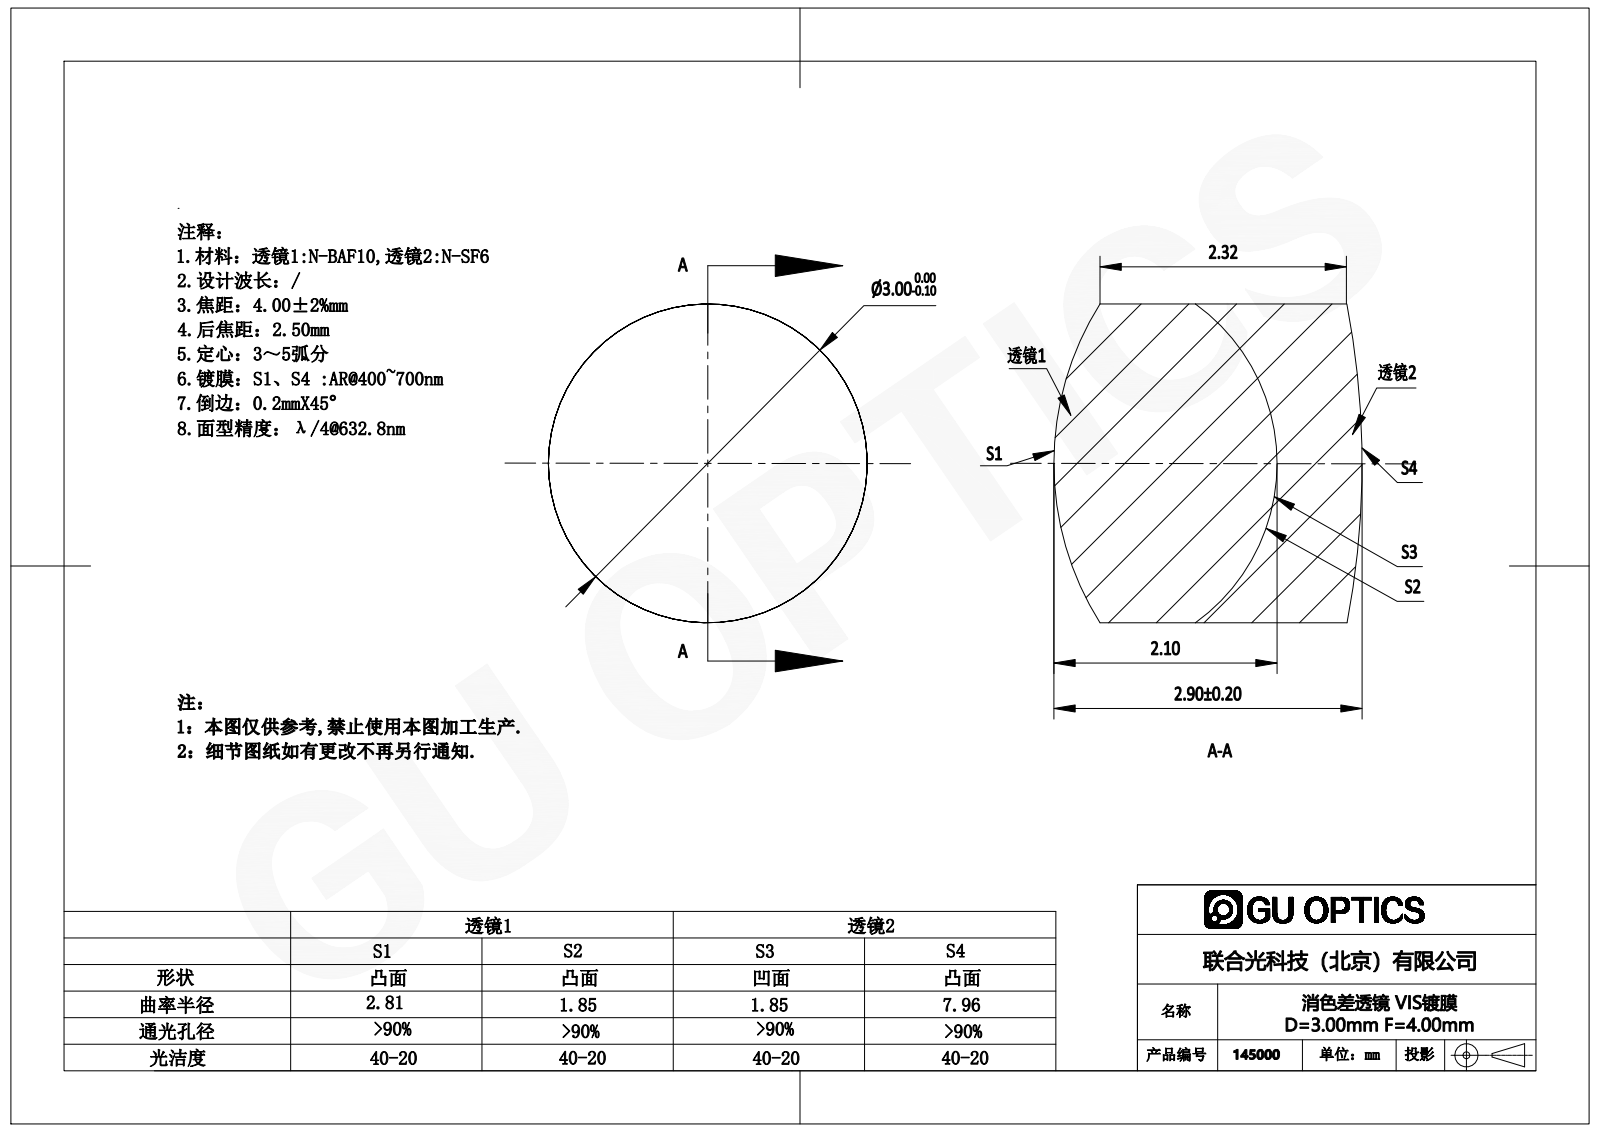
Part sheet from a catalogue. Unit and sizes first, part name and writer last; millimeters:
Units: millimetres
Overall size (bounding box): 3 × 3 × 2.9
Round bosses / shafts (diameter × count): ⌀3 ×1
Volume: 19 mm³ · Surface area: 55 mm²
Bodies: 2 solids, 12 faces (0 planar, 4 cylindrical, 8 other)
Part name (STEP PRODUCT): 145000
STEP written by: SolidWorks 2016 (AUTOMOTIVE_DESIGN)
